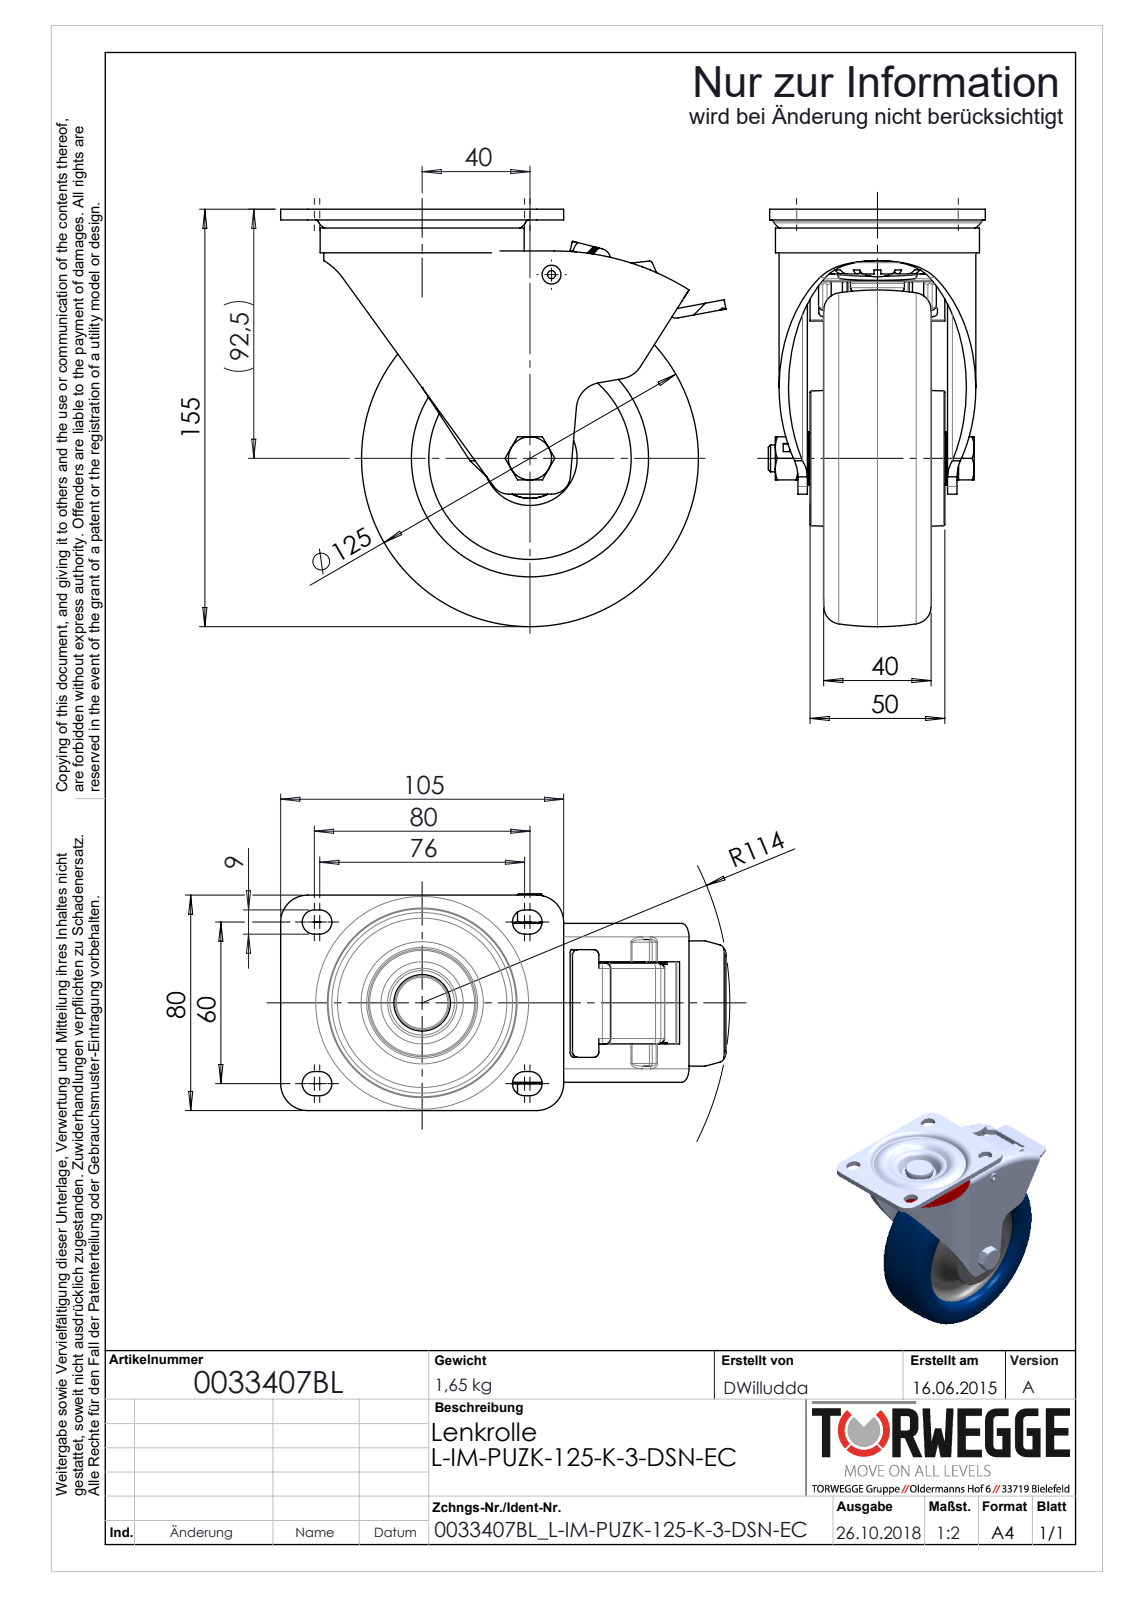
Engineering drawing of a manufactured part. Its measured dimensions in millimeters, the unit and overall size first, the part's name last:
Units: millimetres
Overall size (bounding box): 165.19 × 155 × 80.5
Round holes (diameter × count): ⌀3 ×1, ⌀5 ×1, ⌀5.2 ×1, ⌀8.5 ×1, ⌀10 ×1, ⌀10.35 ×1, ⌀10.5 ×1, ⌀12.5 ×1, ⌀15 ×1, ⌀16 ×1, ⌀29.7 ×1, ⌀35 ×1
Round bosses / shafts (diameter × count): ⌀75.69 ×1, ⌀21 ×1, ⌀19.75 ×1, ⌀14.9 ×1, ⌀12.5 ×1, ⌀7 ×1
Partial cylindrical surfaces — rounded edges, fillets, slot ends (radius × count): R2 ×22, R0.5 ×12, R4.5 ×9, R0.27 ×8, R1.5 ×8, R10 ×8, R0.15 ×7, R0.45 ×7
Main face-to-face distances: 3.5, 55.5, 1, 4, 59, 52, 51, 4.5, 54.5, 1.5
Hole centre spacings: 68.67
Bodies: 0 solids, 1139 faces (568 planar, 278 cylindrical, 293 other)
Part name (STEP PRODUCT): 0033407_L-IM-PUZK-125-K-3-DSN-EC
STEP written by: SolidWorks 2016 (AUTOMOTIVE_DESIGN)
